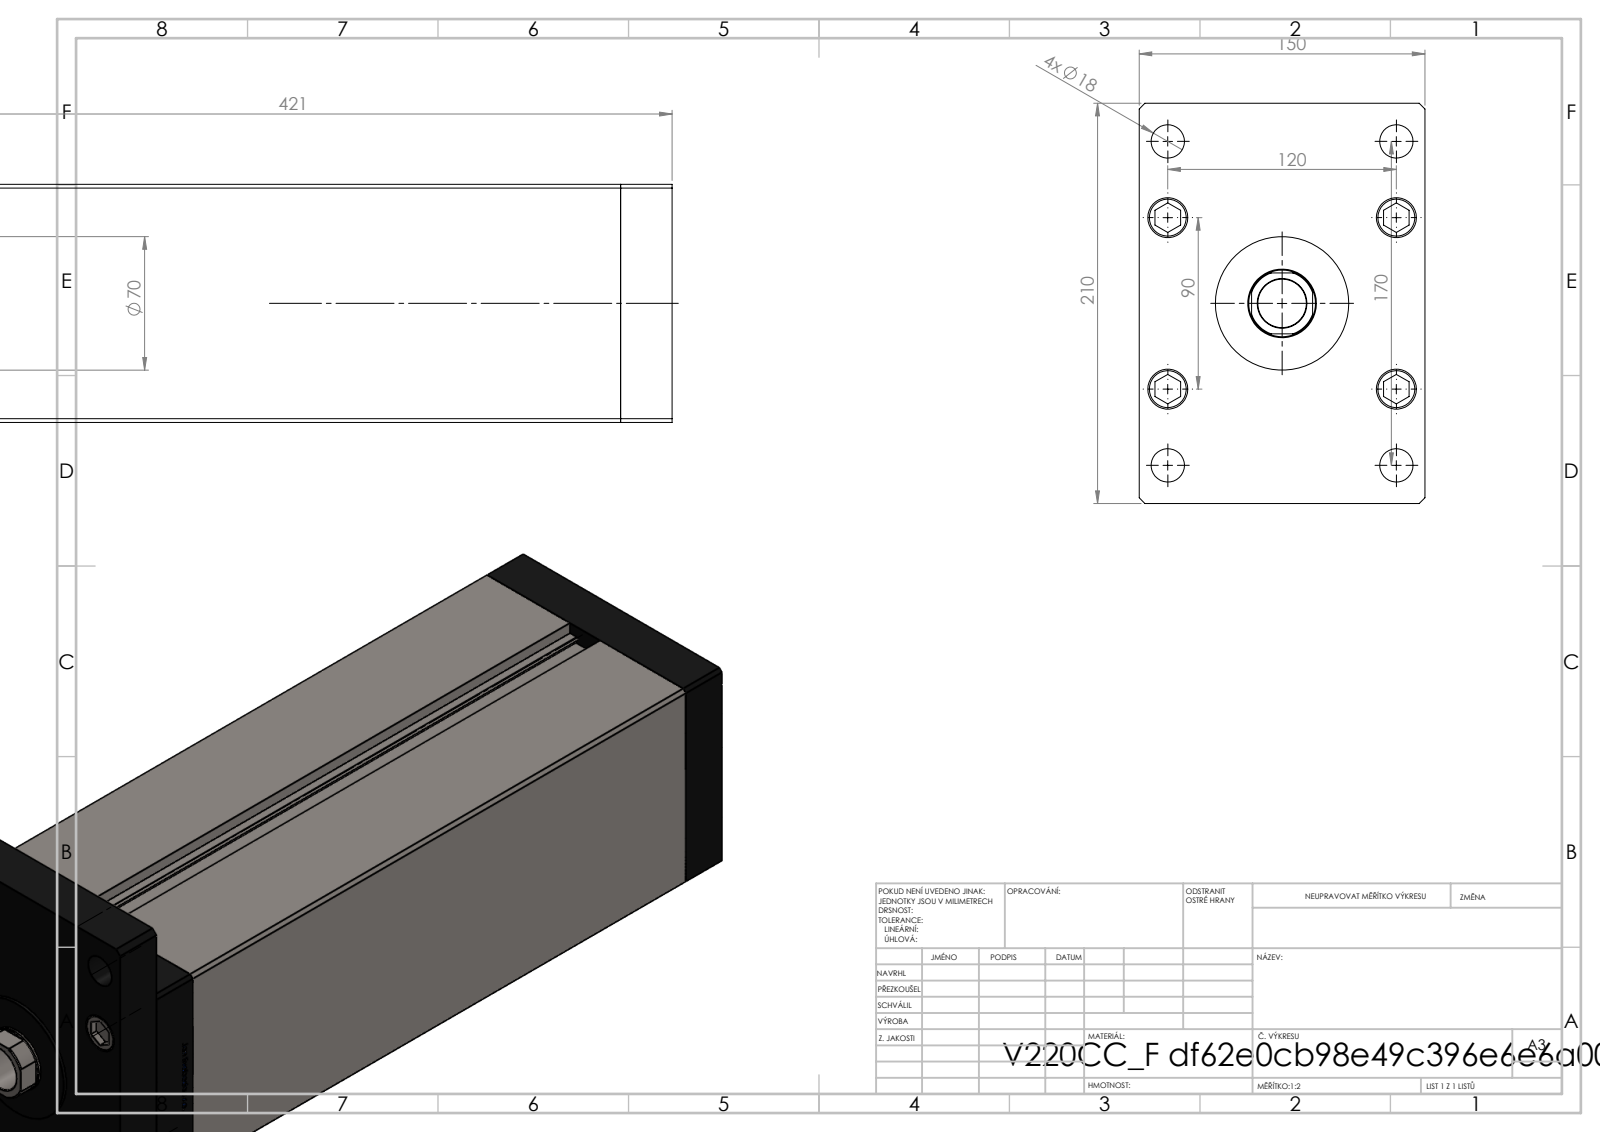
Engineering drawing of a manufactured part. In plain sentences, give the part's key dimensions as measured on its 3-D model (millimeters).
The part is named "V220C_FRONT_F; ALLEN BOLT; V220C_F; V220C_F_MIDDLE (+2 more)". Its 3-D file was written by "SolidWorks 2019 (CONFIG_CONTROL_DESIGN)". It is 19 solids with 1310 faces: 517 planar, 187 cylindrical and 606 other. Overall it measures 463 by 210 by 150 millimeters. Its volume is 7 271 000 cubic millimeters and its surface area 658 891 square millimeters. Round holes: 9 of diameter 17.5, 5 of diameter 22, 4 of diameter 16, 4 of diameter 21, 2 of diameter 2, 2 of diameter 13.16, 1 of diameter 25.5, 1 of diameter 36, 1 of diameter 37.5. Round bosses or shafts: 9 of diameter 8, 5 of diameter 21, 1 of diameter 80, 1 of diameter 70. Partial cylindrical surfaces (rounded edges, fillets, slot ends): 2 of radius 0.93, 1 of radius 17.5. The main face-to-face distances are 27, 150, 125, 394, 421, 367, 54, 448, 33.5, 6.5. The hole center spacings are 51, 40, 75, 104.04, 120, 126.49, 130, 176.92.
